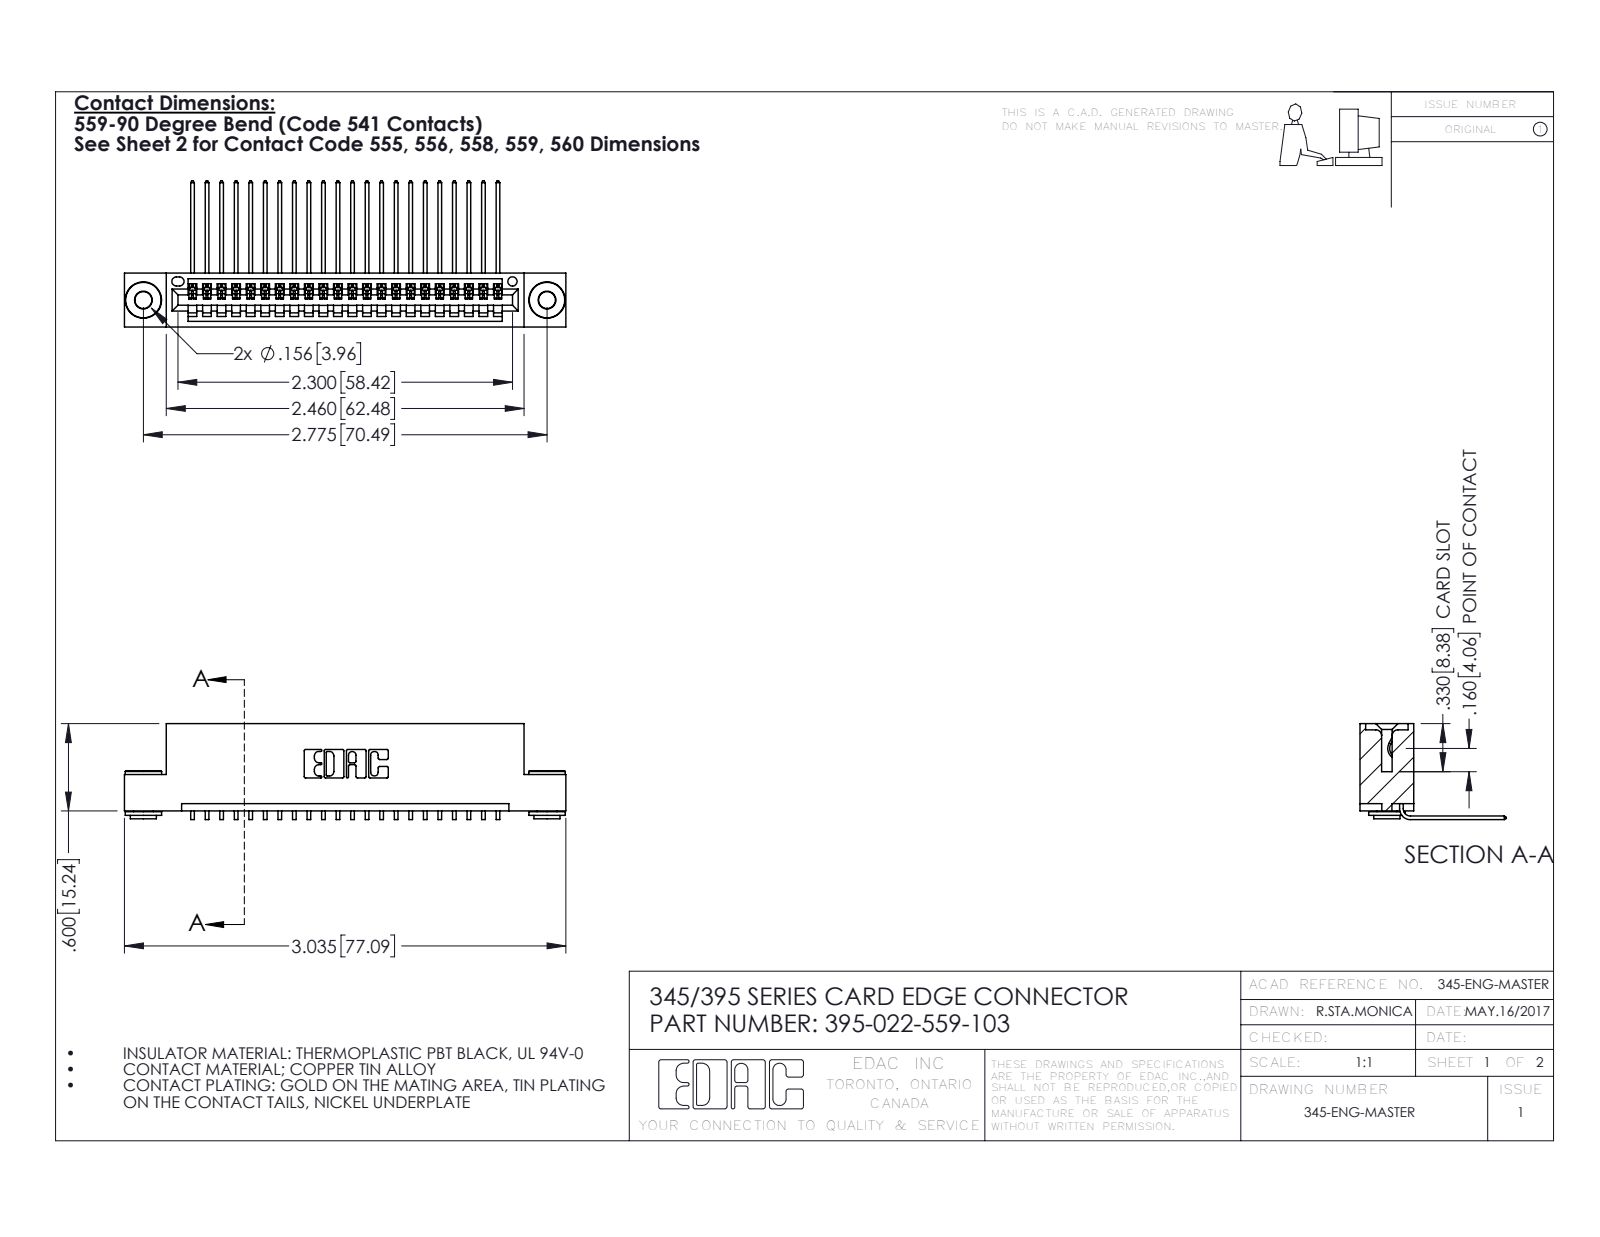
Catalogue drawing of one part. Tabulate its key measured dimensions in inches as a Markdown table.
| quantity | value |
| --- | --- |
| part name | 345 Part_Flush Mounting Lugs - 0.156 Dia-TH; 345-250-002_345-250-002-102; 345-292-001_558 559 Tail - 1; 395-022-559-103 |
| STEP written by | SolidWorks 2016 (CONFIG_CONTROL_DESIGN) |
| units | inches |
| bodies | 25 solids, 1484 faces (1014 planar, 462 cylindrical, 8 other) |
| overall size | 3.035 × 1.005 × 0.659 |
| volume | 0.442 in³ |
| surface area | 15.51 in² |
| round holes (diameter × count) | 0.116 × 2, 0.156 × 2, 0.064 × 1 |
| round bosses / shafts (diameter × count) | 0.25 × 2, 0.18 × 2, 0.136 × 2 |
| partial cylindrical surfaces (radius × count) | 0.006 × 44, 0.01 × 22, 0.007 × 6, 0.031 × 6, 0.026 × 3, 0.031 × 2, 0.04 × 2, 0.014 × 1 |
| main face-to-face distances | 0.072, 0.298, 0.2, 0.37, 0.025, 0.098, 0.272, 0.225, 0.149, 0.072 |
| hole center spacings | 0.27, 2.541, 2.775 |
